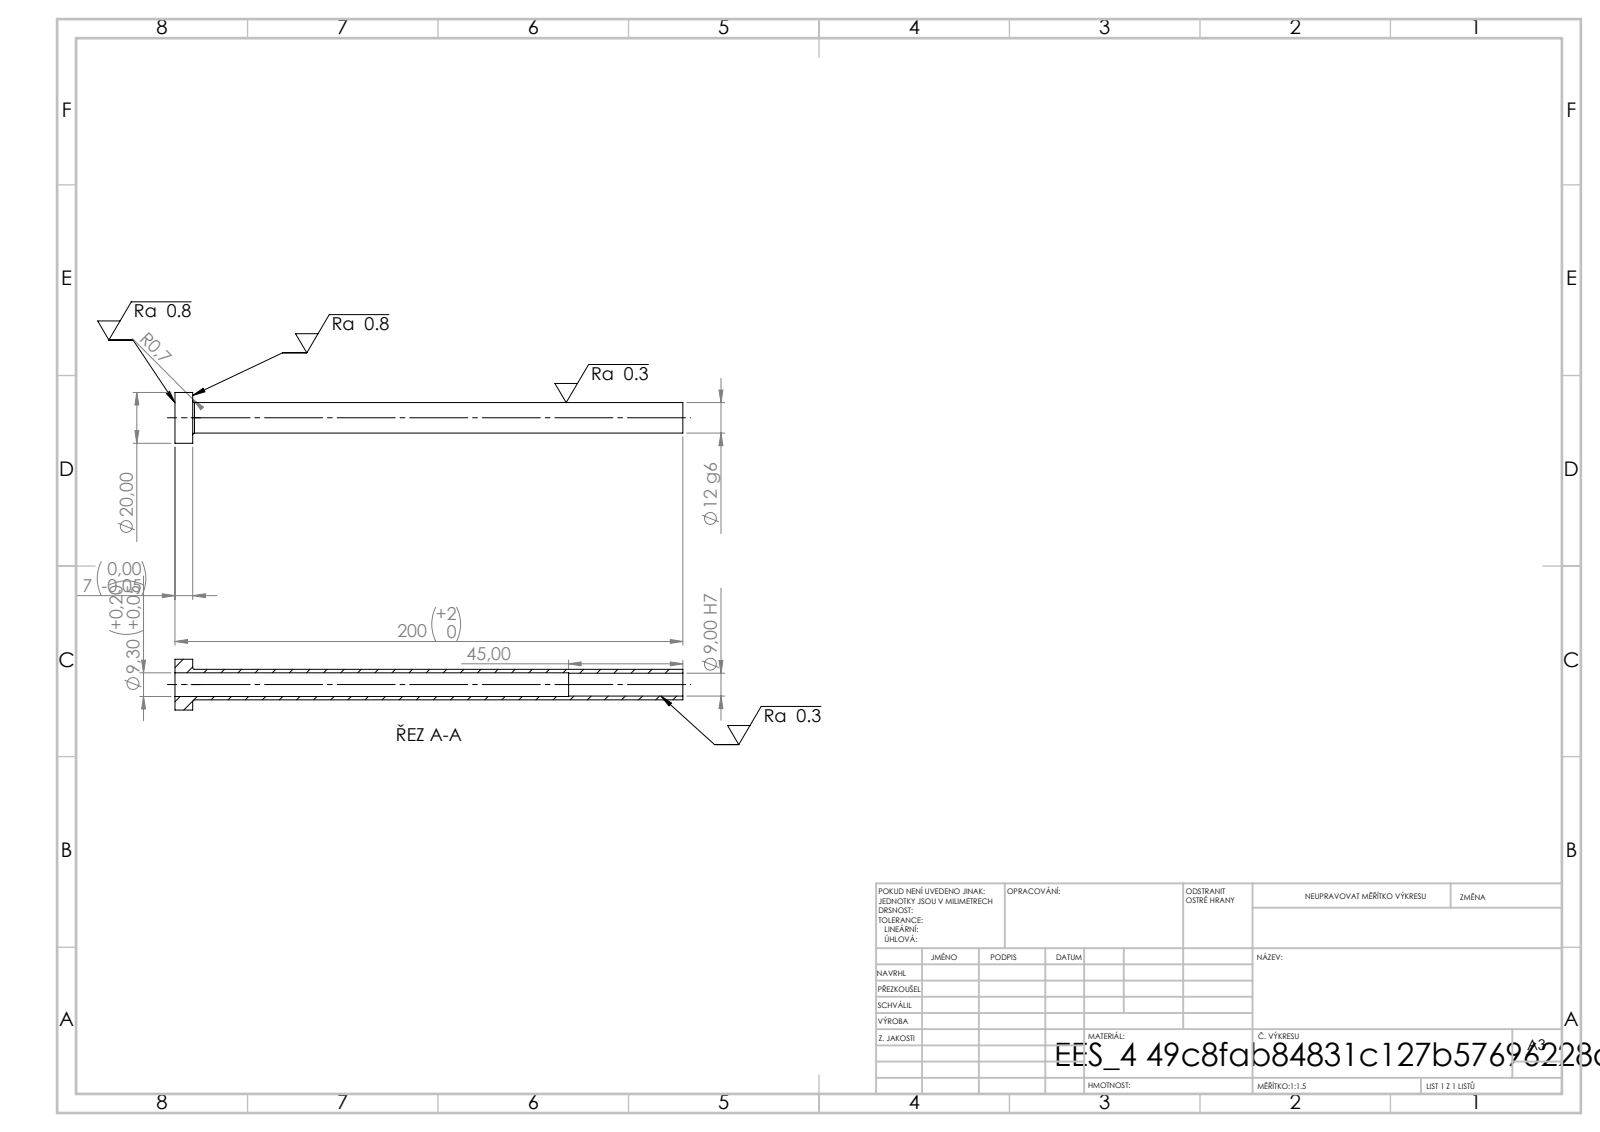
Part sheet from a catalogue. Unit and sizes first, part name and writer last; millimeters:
Units: millimetres
Overall size (bounding box): 200 × 20 × 20
Round holes (diameter × count): ⌀9 ×1, ⌀9.3 ×1
Round bosses / shafts (diameter × count): ⌀20 ×1, ⌀12 ×1
Main face-to-face distances: 7, 200, 193, 155, 148, 45
Volume: 10 639 mm³ · Surface area: 14 007 mm²
Bodies: 1 solid, 14 faces (4 planar, 8 cylindrical, 2 other)
STEP written by: SolidWorks 2019 (CONFIG_CONTROL_DESIGN)
